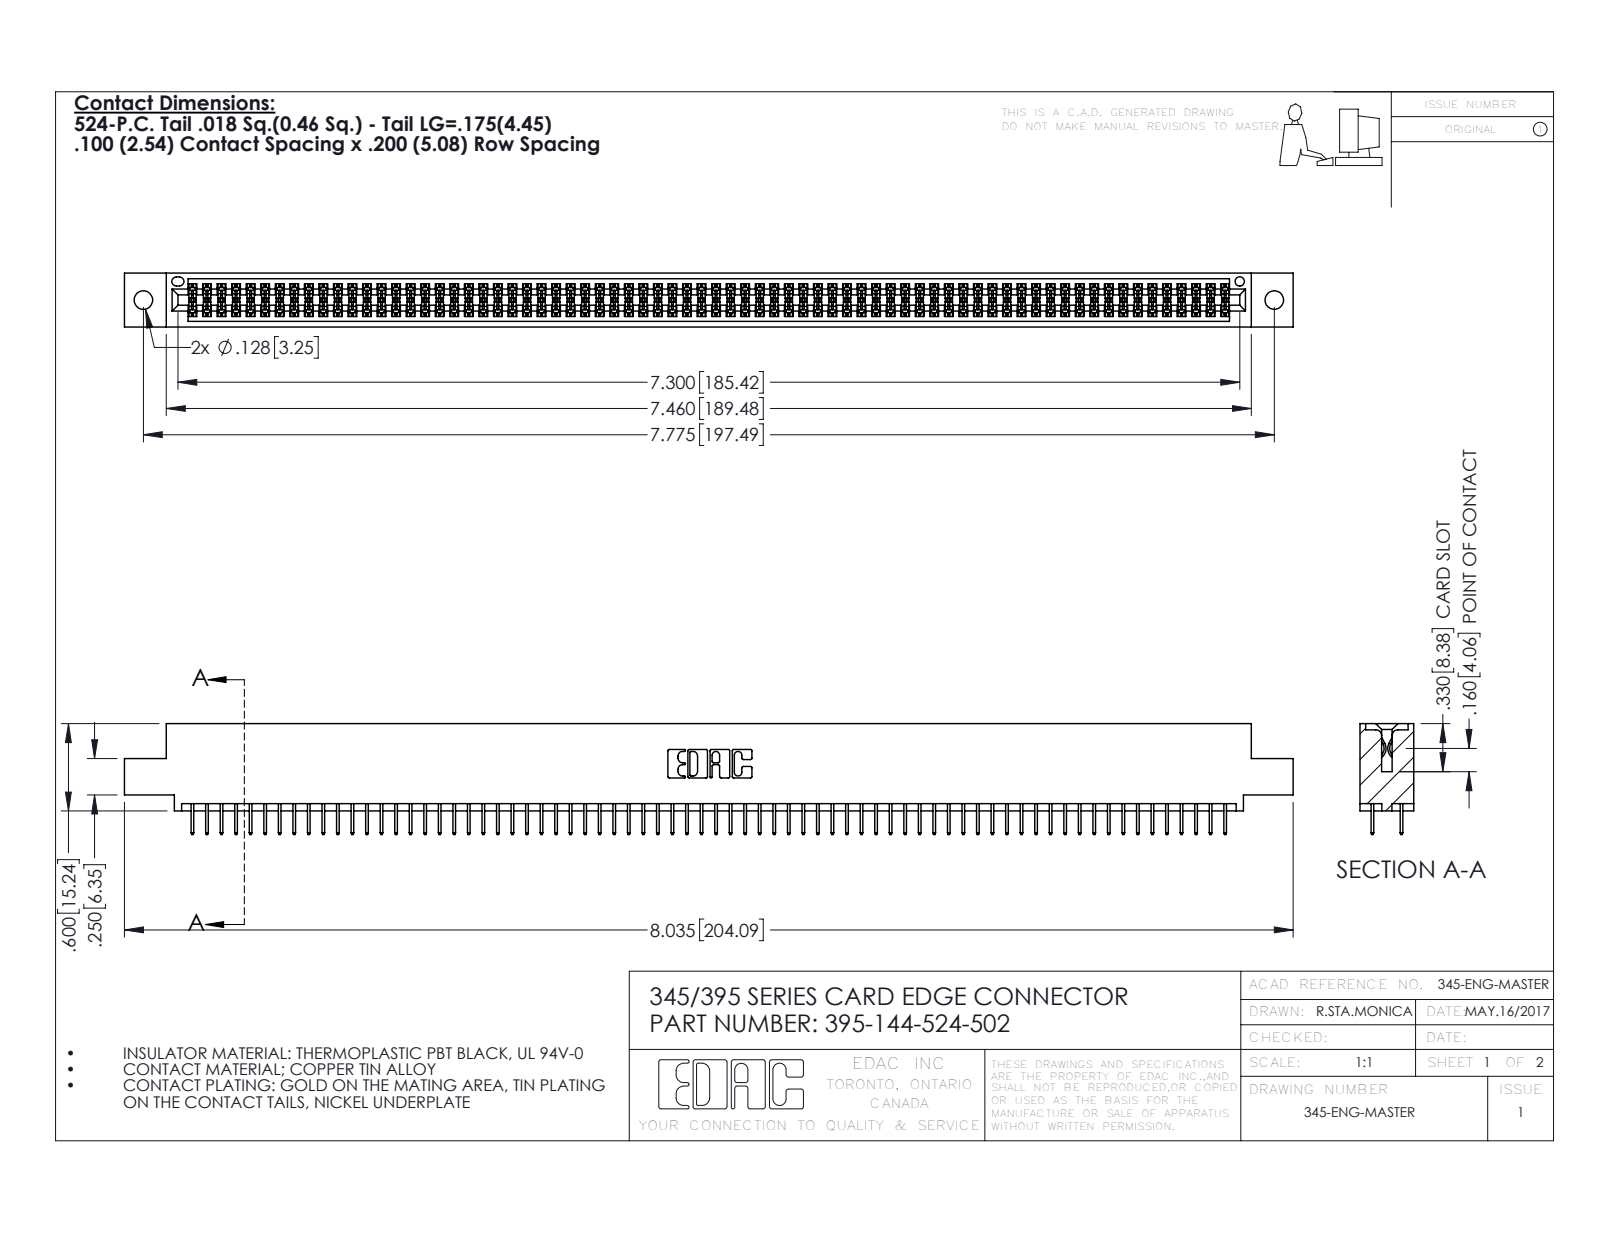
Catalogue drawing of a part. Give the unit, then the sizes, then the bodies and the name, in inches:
Units: inches
Overall size (bounding box): 8.035 × 0.762 × 0.37
Round holes (diameter × count): ⌀0.128 ×2, ⌀0.064 ×1
Partial cylindrical surfaces — rounded edges, fillets, slot ends (radius × count): R0.006 ×216, R0.01 ×22, R0.007 ×6, R0.031 ×6, R0.026 ×3, R0.014 ×2, R0.019 ×2, R0.022 ×2
Main face-to-face distances: 0.072, 0.298, 0.2, 0.37, 0.098, 0.272, 0.025, 0.225, 0.072, 0.175
Hole centre spacings: 0.27, 7.539, 7.775
Volume: 1.207 in³ · Surface area: 45.04 in²
Bodies: 145 solids, 7906 faces (5700 planar, 2206 cylindrical, 0 other)
Part name (STEP PRODUCT): 345-292-001_345-293-124; 345 Part_0.110 Offset - 0.128 Dia; 395-144-524-502
STEP written by: SolidWorks 2016 (CONFIG_CONTROL_DESIGN)
